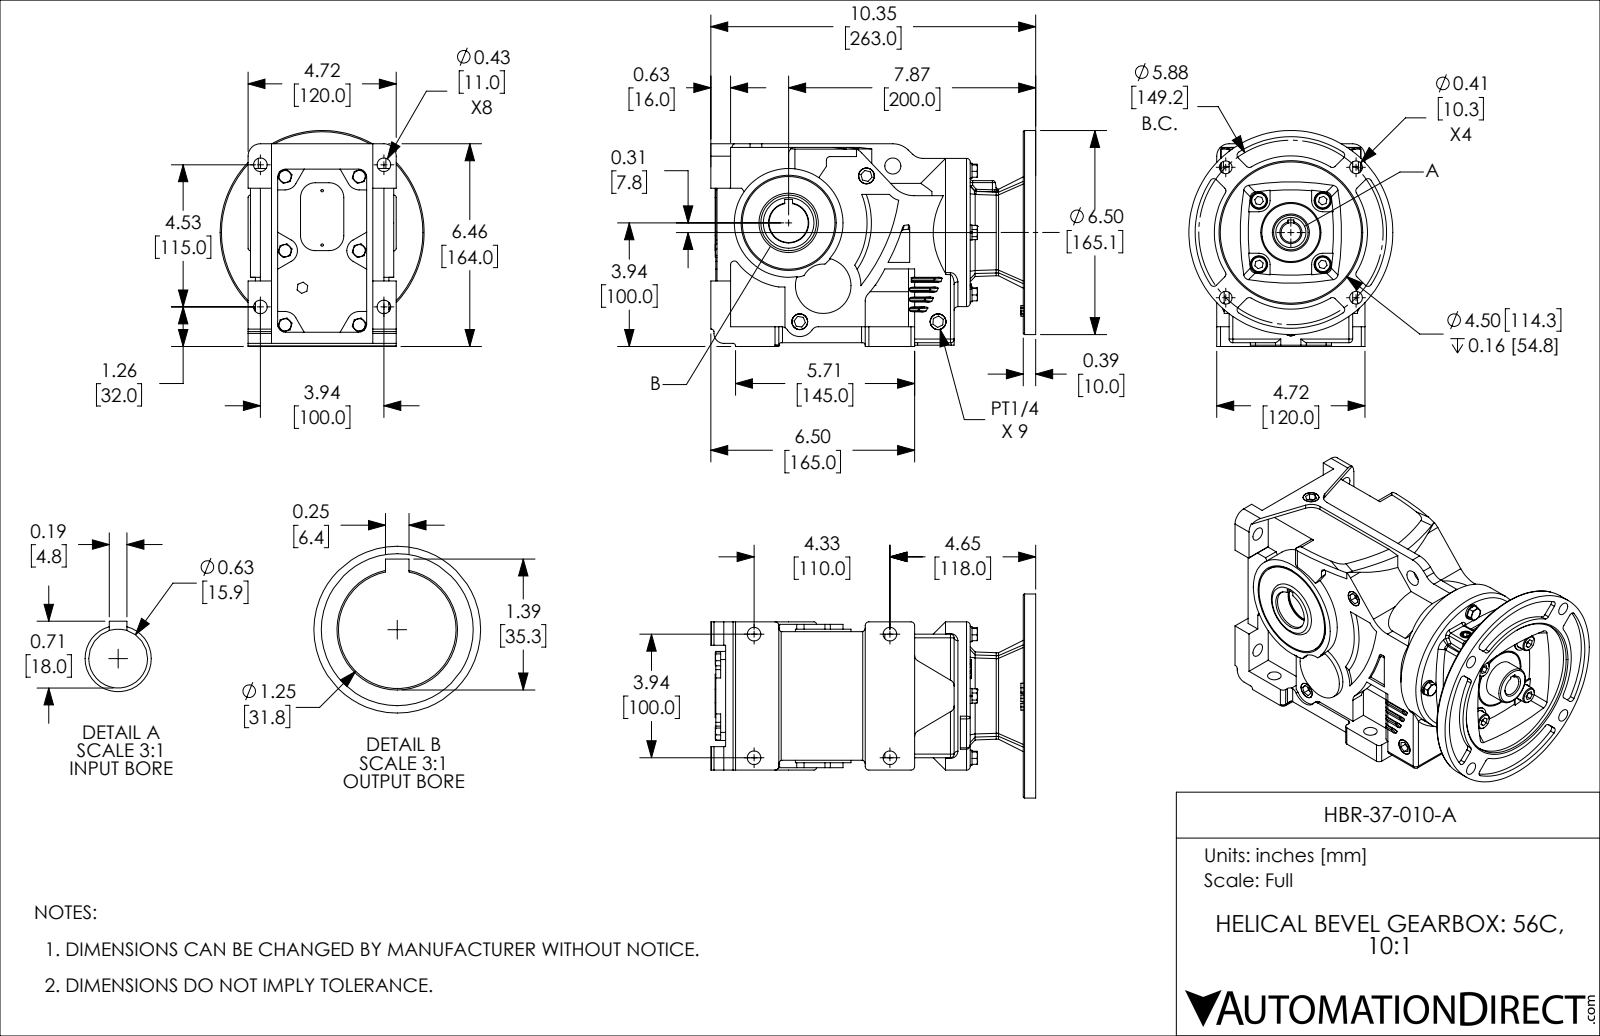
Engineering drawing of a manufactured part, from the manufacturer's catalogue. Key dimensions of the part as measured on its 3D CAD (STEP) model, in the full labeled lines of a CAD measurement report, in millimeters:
Part name (STEP PRODUCT): HBR-37-010-A
STEP written by: SolidWorks 2018 (AUTOMOTIVE_DESIGN)
Units: millimetres
Bodies: 1 solid, 1082 faces (491 planar, 289 cylindrical, 302 other)
Overall size (bounding box): 263 × 174.8 × 165.1
Volume: 3 292 000 mm³ · Surface area: 252 100 mm²
Round holes (diameter × count): ⌀11 ×8, ⌀6.1 ×4, ⌀7 ×4, ⌀10.3 ×4, ⌀14 ×4, ⌀2 ×2, ⌀13 ×1, ⌀15.9 ×1, ⌀21.5 ×1, ⌀31.8 ×1, ⌀33.7 ×1, ⌀114.3 ×1
Round bosses / shafts (diameter × count): ⌀13 ×4, ⌀12.2 ×4, ⌀6 ×4, ⌀165.1 ×1, ⌀120 ×1, ⌀88 ×1, ⌀75 ×1, ⌀47 ×1
Partial cylindrical surfaces — rounded edges, fillets, slot ends (radius × count): R3 ×42, R1 ×18, R5 ×11, R2 ×10, R10 ×10, R12 ×6, R6.5 ×4, R9 ×4
Main face-to-face distances: 4, 10, 12, 8, 6, 3, 2, 108, 16, 96
Hole centre spacings: 35.4, 52.8, 80.1, 83.1, 115.5, 100, 36.5, 38.1
